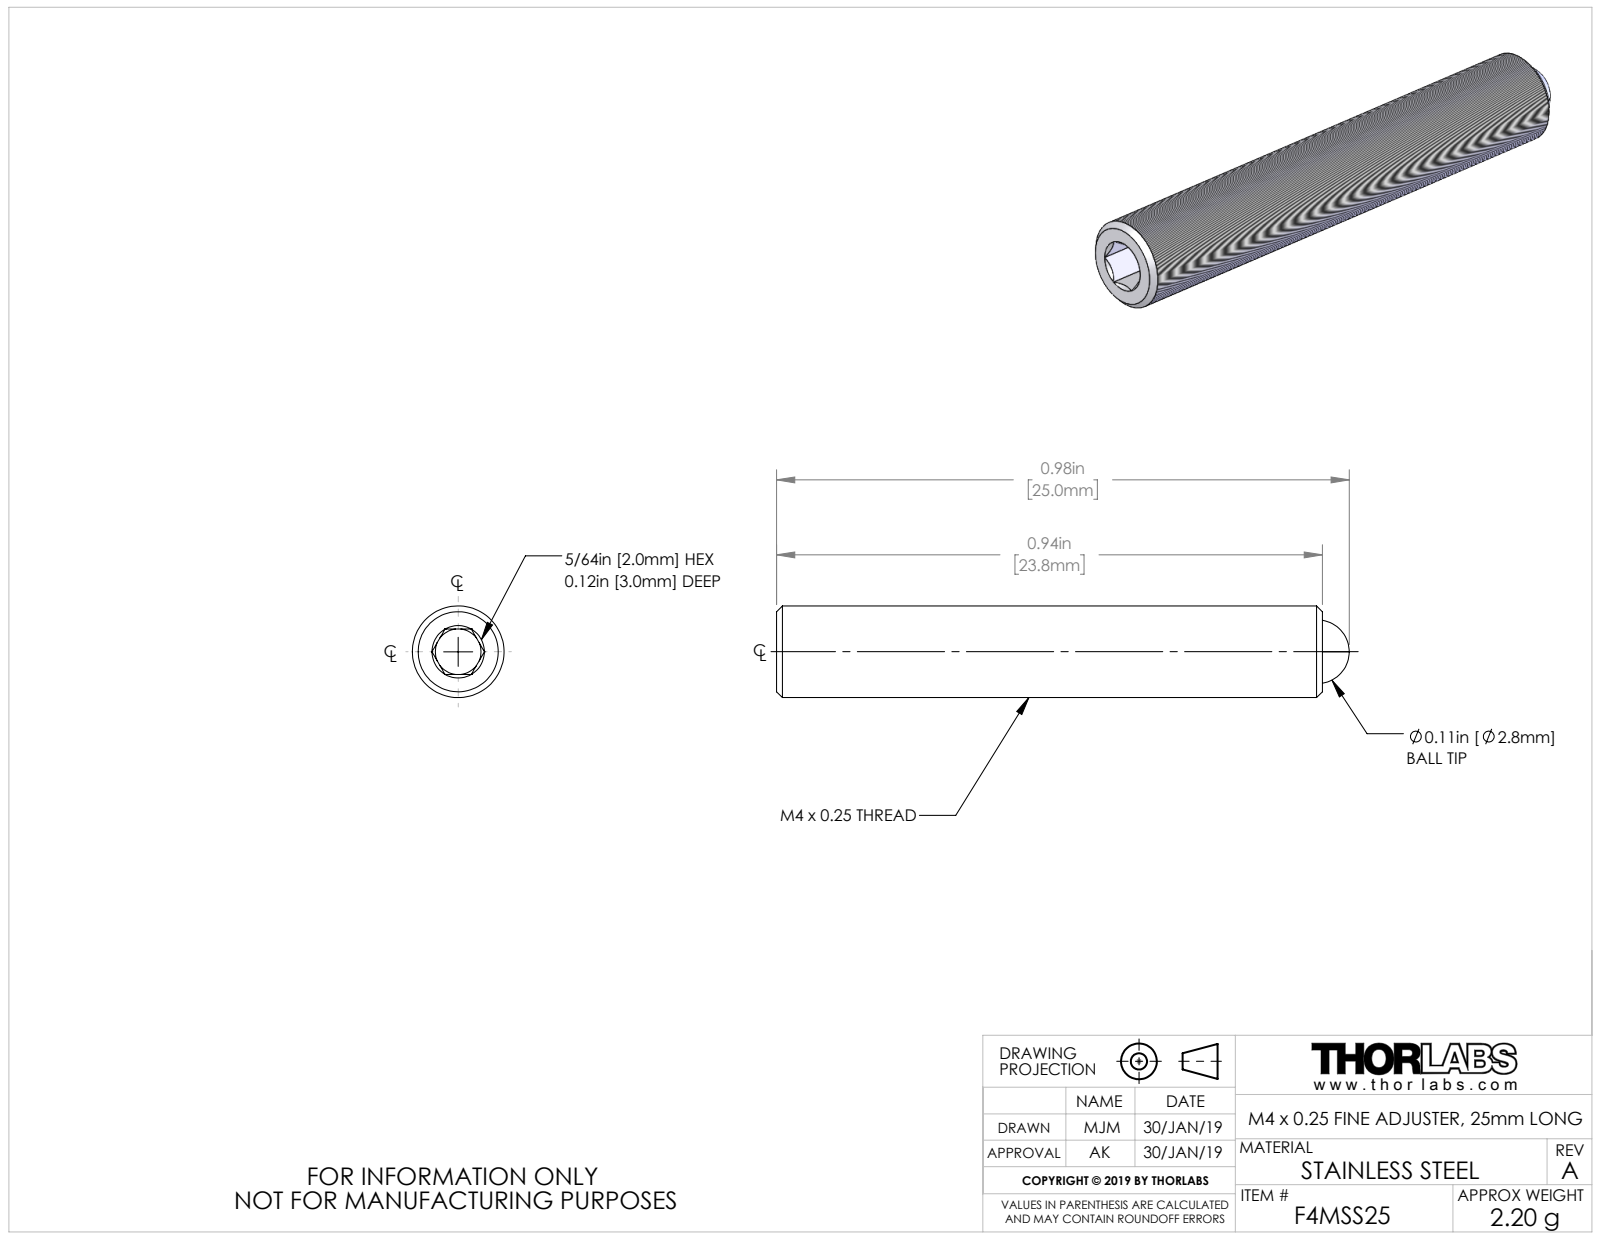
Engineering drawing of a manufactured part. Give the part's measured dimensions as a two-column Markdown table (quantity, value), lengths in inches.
| quantity | value |
| --- | --- |
| part name | TTN174705-E0W |
| STEP written by | SolidWorks 2018 (AUTOMOTIVE_DESIGN) |
| units | inches |
| bodies | 2 solids, 45 faces (20 planar, 6 cylindrical, 19 other) |
| overall size | 0.984 × 0.157 × 0.157 |
| volume | 0.018 in³ |
| surface area | 0.591 in² |
| round holes (diameter × count) | 0.079 × 1, 0.11 × 1 |
| round bosses / shafts (diameter × count) | 0.157 × 1 |
| main face-to-face distances | 0.078, 0.938, 0.818, 0.12 |
